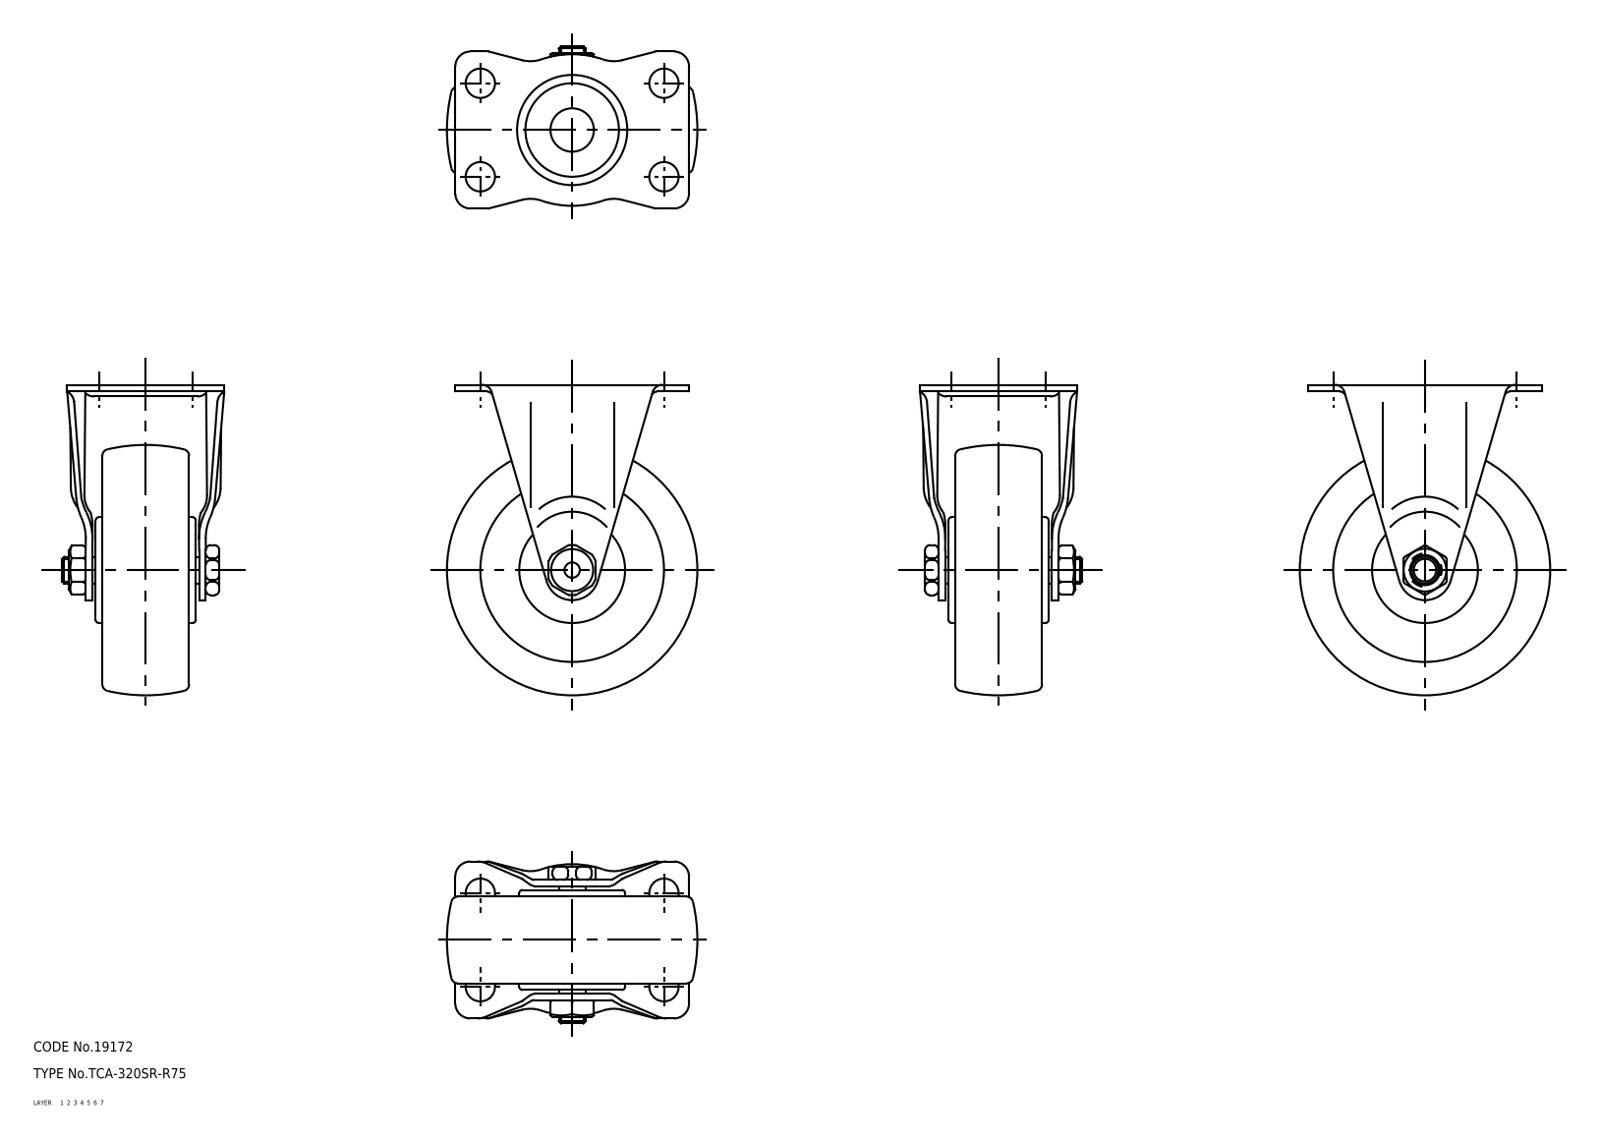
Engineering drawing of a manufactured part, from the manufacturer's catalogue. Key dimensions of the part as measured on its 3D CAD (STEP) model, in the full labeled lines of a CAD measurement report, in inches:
Part name (STEP PRODUCT): wheel; axle; 320SR_R75_8602_36
STEP written by: CADfix (AUTOMOTIVE_DESIGN)
Units: inches
Bodies: 3 solids, 239 faces (0 planar, 0 cylindrical, 239 other)
Overall size (bounding box): 3.661 × 2.953 × 1.909
Volume: 7.843 in³ · Surface area: 48.96 in²
